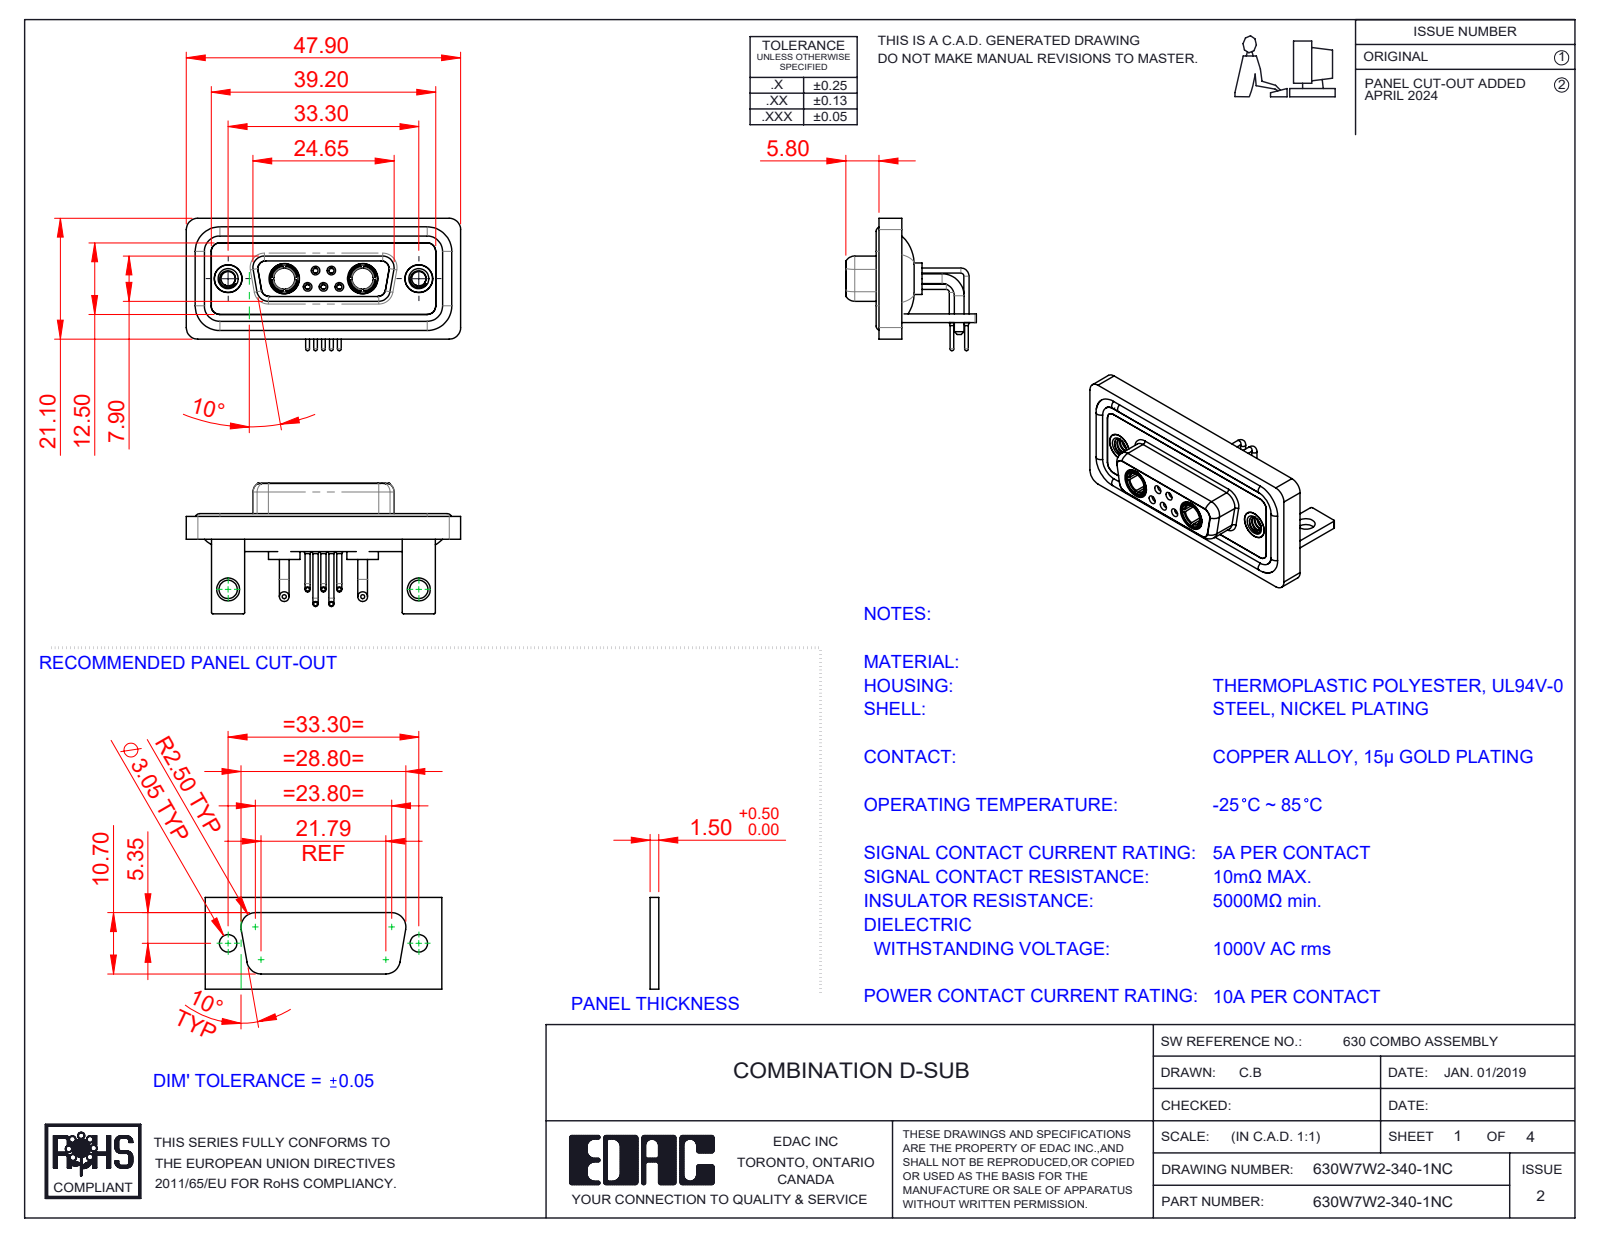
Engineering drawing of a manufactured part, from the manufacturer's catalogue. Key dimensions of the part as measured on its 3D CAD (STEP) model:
Part name (STEP PRODUCT): 630Combo Contact Row 1_50 Contacts; 630Combo Housing_7W2; 630Combo Waterproof Housing_15 Contacts; 630Combo Stabilizer Bracket_50 Contacts (+6 more)
STEP written by: SolidWorks 2023 (CONFIG_CONTROL_DESIGN)
Units: millimetres
Bodies: 18 solids, 849 faces (258 planar, 375 cylindrical, 216 other)
Overall size (bounding box): 47.9 × 23.12 × 22.8
Volume: 6 440 mm³ · Surface area: 10 843 mm²
Round holes (diameter × count): ⌀0.9 ×5, ⌀1.1 ×5, ⌀1.5 ×5, ⌀2 ×5, ⌀4.85 ×4, ⌀1.6 ×3, ⌀1.7 ×2, ⌀2.5 ×2, ⌀3.2 ×2, ⌀3.7 ×2, ⌀4 ×2, ⌀4.05 ×2
Round bosses / shafts (diameter × count): ⌀1.6 ×6, ⌀0.9 ×5, ⌀0.65 ×5, ⌀1.7 ×4, ⌀5.5 ×2, ⌀5.2 ×2, ⌀4.96 ×2, ⌀4.95 ×2
Partial cylindrical surfaces — rounded edges, fillets, slot ends (radius × count): R2 ×21, R1.5 ×18, R0.25 ×16, R1.35 ×12, R1.6 ×8, R0.5 ×5, R0.6 ×4, R0.65 ×4
Main face-to-face distances: 0.4, 2.9, 1.5, 1.8, 3.7, 1.1, 4.1, 1.6, 2.5, 1.4
Hole centre spacings: 3.16, 2.77, 9.8, 23.5, 33.3, 4.31, 4.33, 5.03
